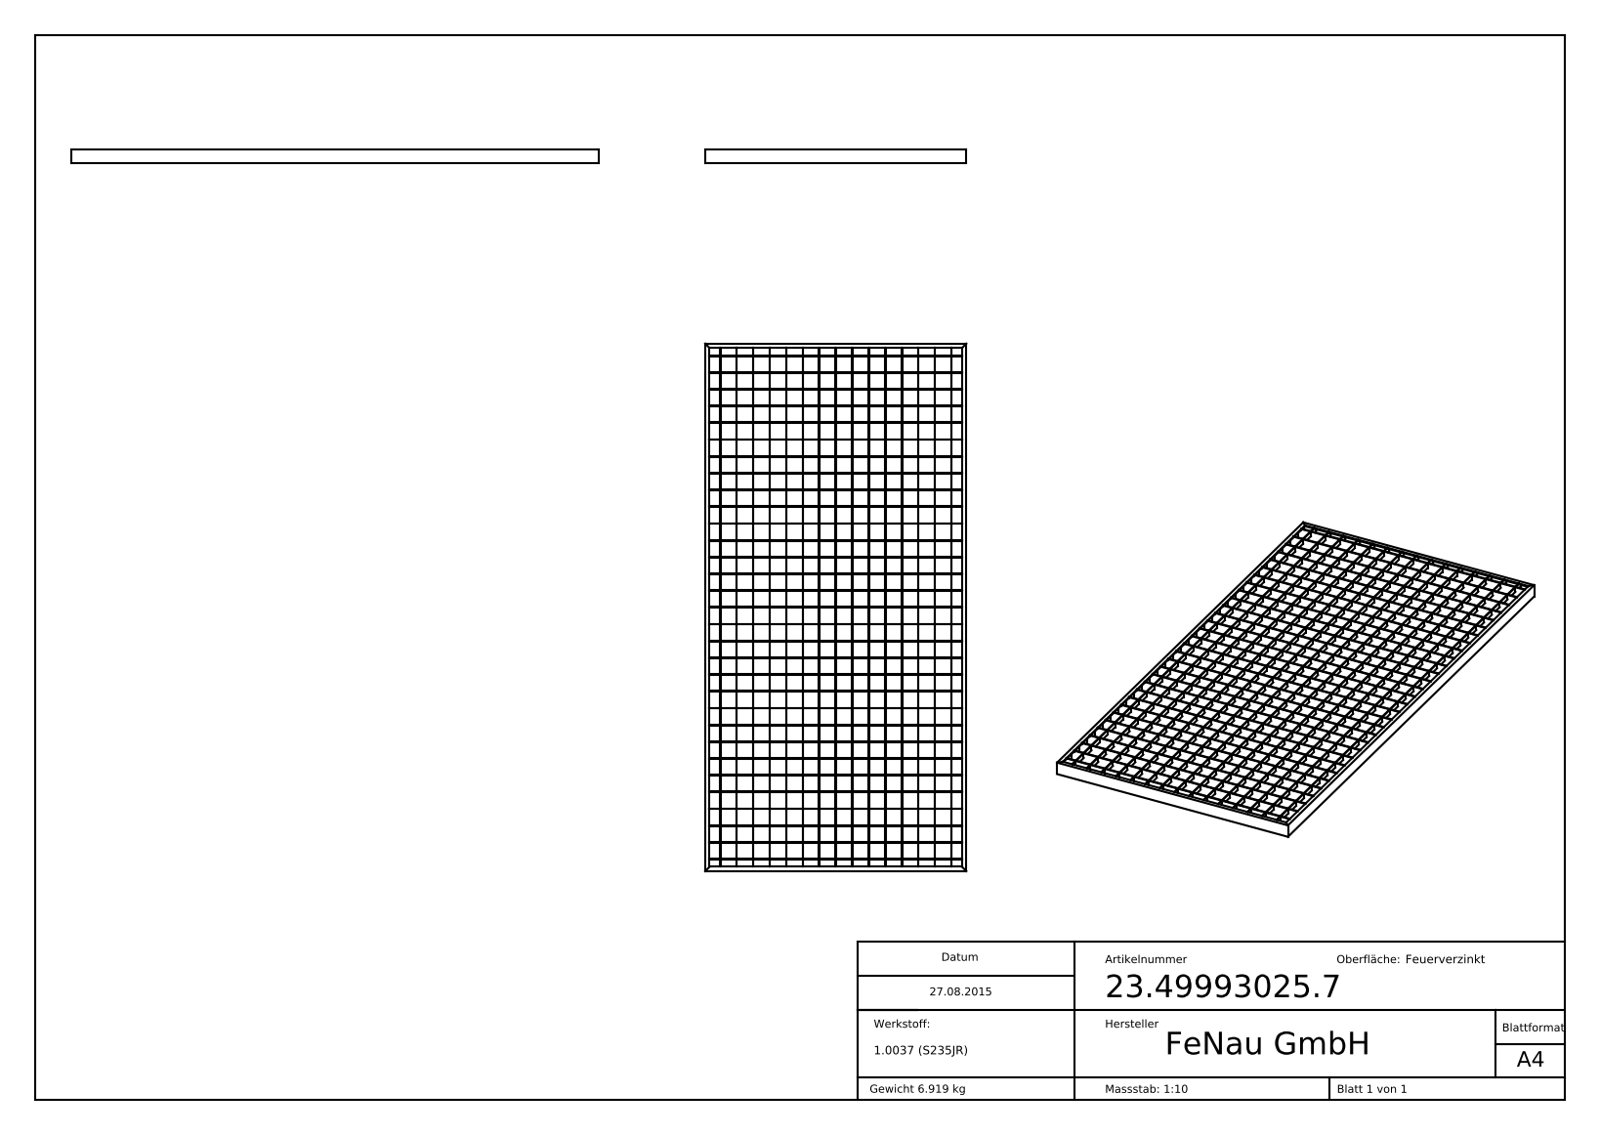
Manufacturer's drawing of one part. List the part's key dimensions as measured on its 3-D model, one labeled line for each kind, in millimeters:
Part name (STEP PRODUCT): 23-49993025-7
STEP written by: SolidWorks 2015 (CONFIG_CONTROL_DESIGN)
Units: millimetres
Bodies: 1 solid, 1768 faces (1768 planar, 0 cylindrical, 0 other)
Overall size (bounding box): 990 × 490 × 25
Volume: 887 064 mm³ · Surface area: 1 287 000 mm²
Main face-to-face distances: 63, 31.5, 94.5, 126, 157.5, 31, 189, 220.5, 252, 283.5
